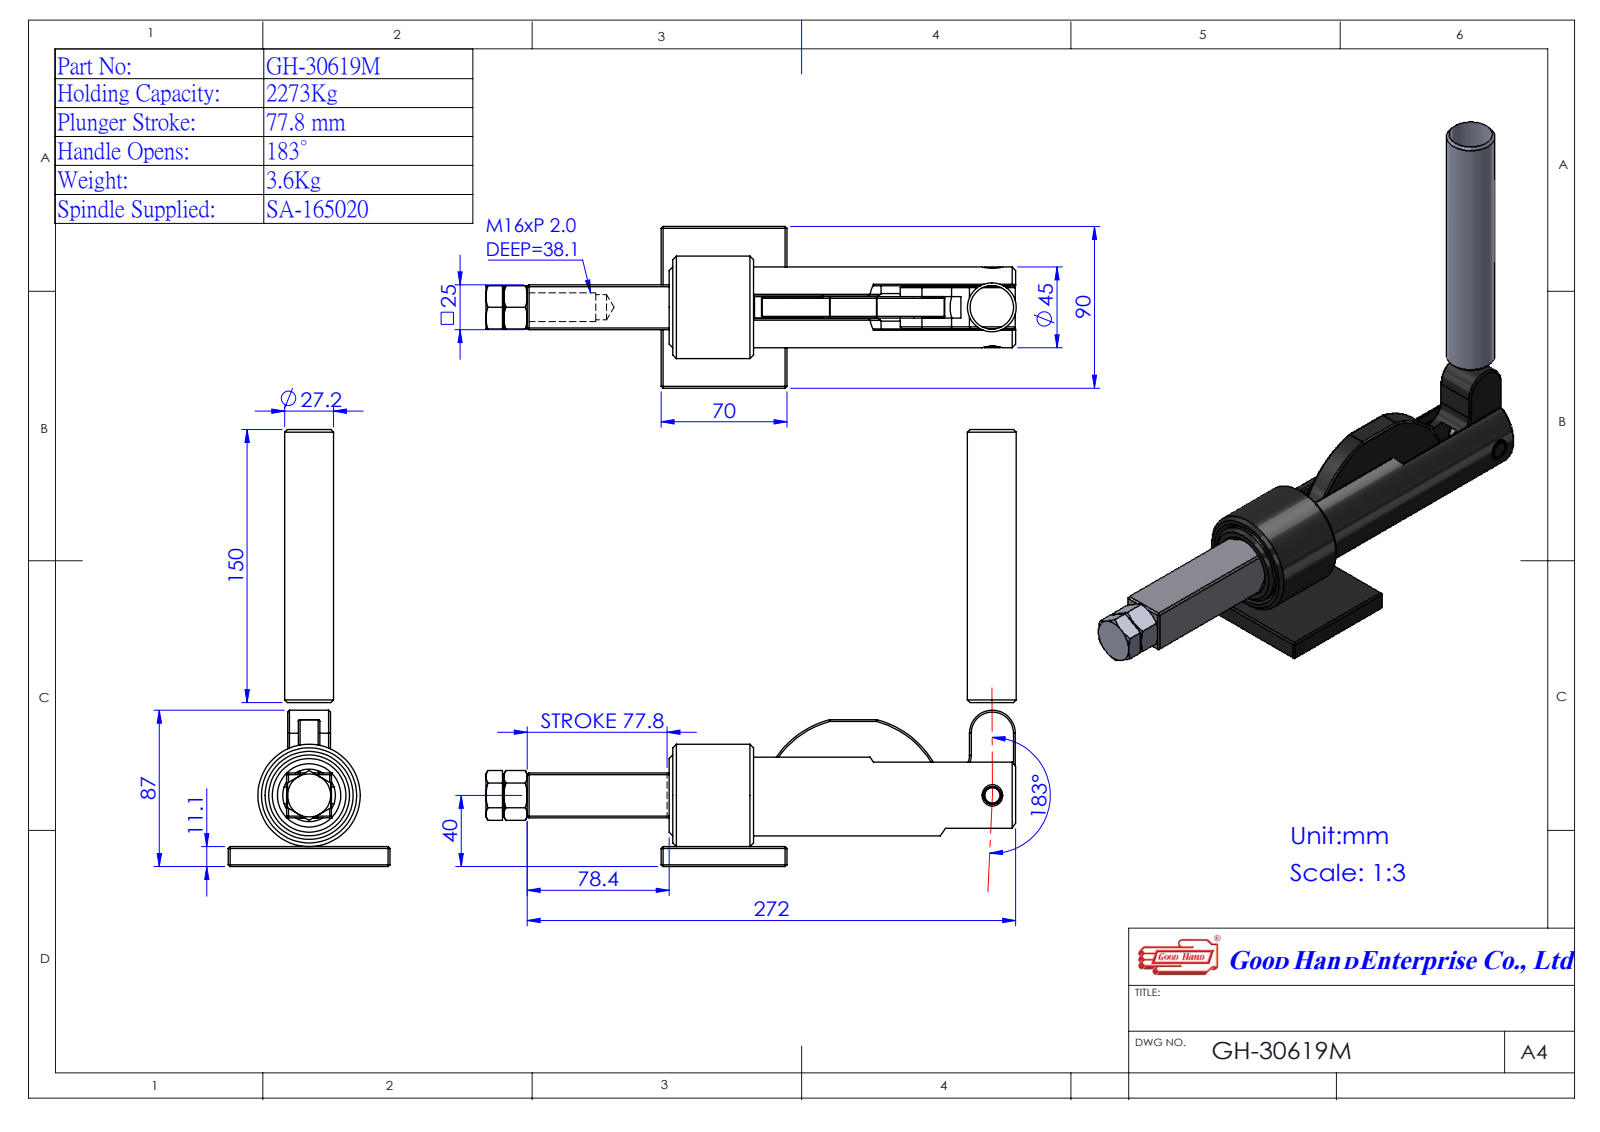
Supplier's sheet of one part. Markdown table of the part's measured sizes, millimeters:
| quantity | value |
| --- | --- |
| part name | 4702K152-1^GH-30609M(簡化); 3302505-1^GH-30619M(簡化); GH-30619M(簡化); Group4^GH-30609M(簡化) (+4 more) |
| STEP written by | SolidWorks 2016 (AUTOMOTIVE_DESIGN) |
| units | millimeters |
| bodies | 8 solids, 151 faces (74 planar, 49 cylindrical, 28 other) |
| overall size | 294.44 × 239.38 × 90 |
| volume | 466 004 mm³ |
| surface area | 148 377 mm² |
| round holes (diameter × count) | 7.5 × 3, 14 × 1, 21.7 × 1, 45 × 1 |
| round bosses / shafts (diameter × count) | 57 × 1, 27.2 × 1, 24 × 1, 16 × 1 |
| partial cylindrical surfaces (radius × count) | 10 × 2, 12.5 × 2, 12 × 1, 12.75 × 1, 14.65 × 1, 29 × 1, 52 × 1 |
| main face-to-face distances | 25, 6.5, 18.5, 11.1, 12, 27.1, 16, 52.1, 41, 0.6 |
| hole center spacings | 39, 77, 115.99 |
